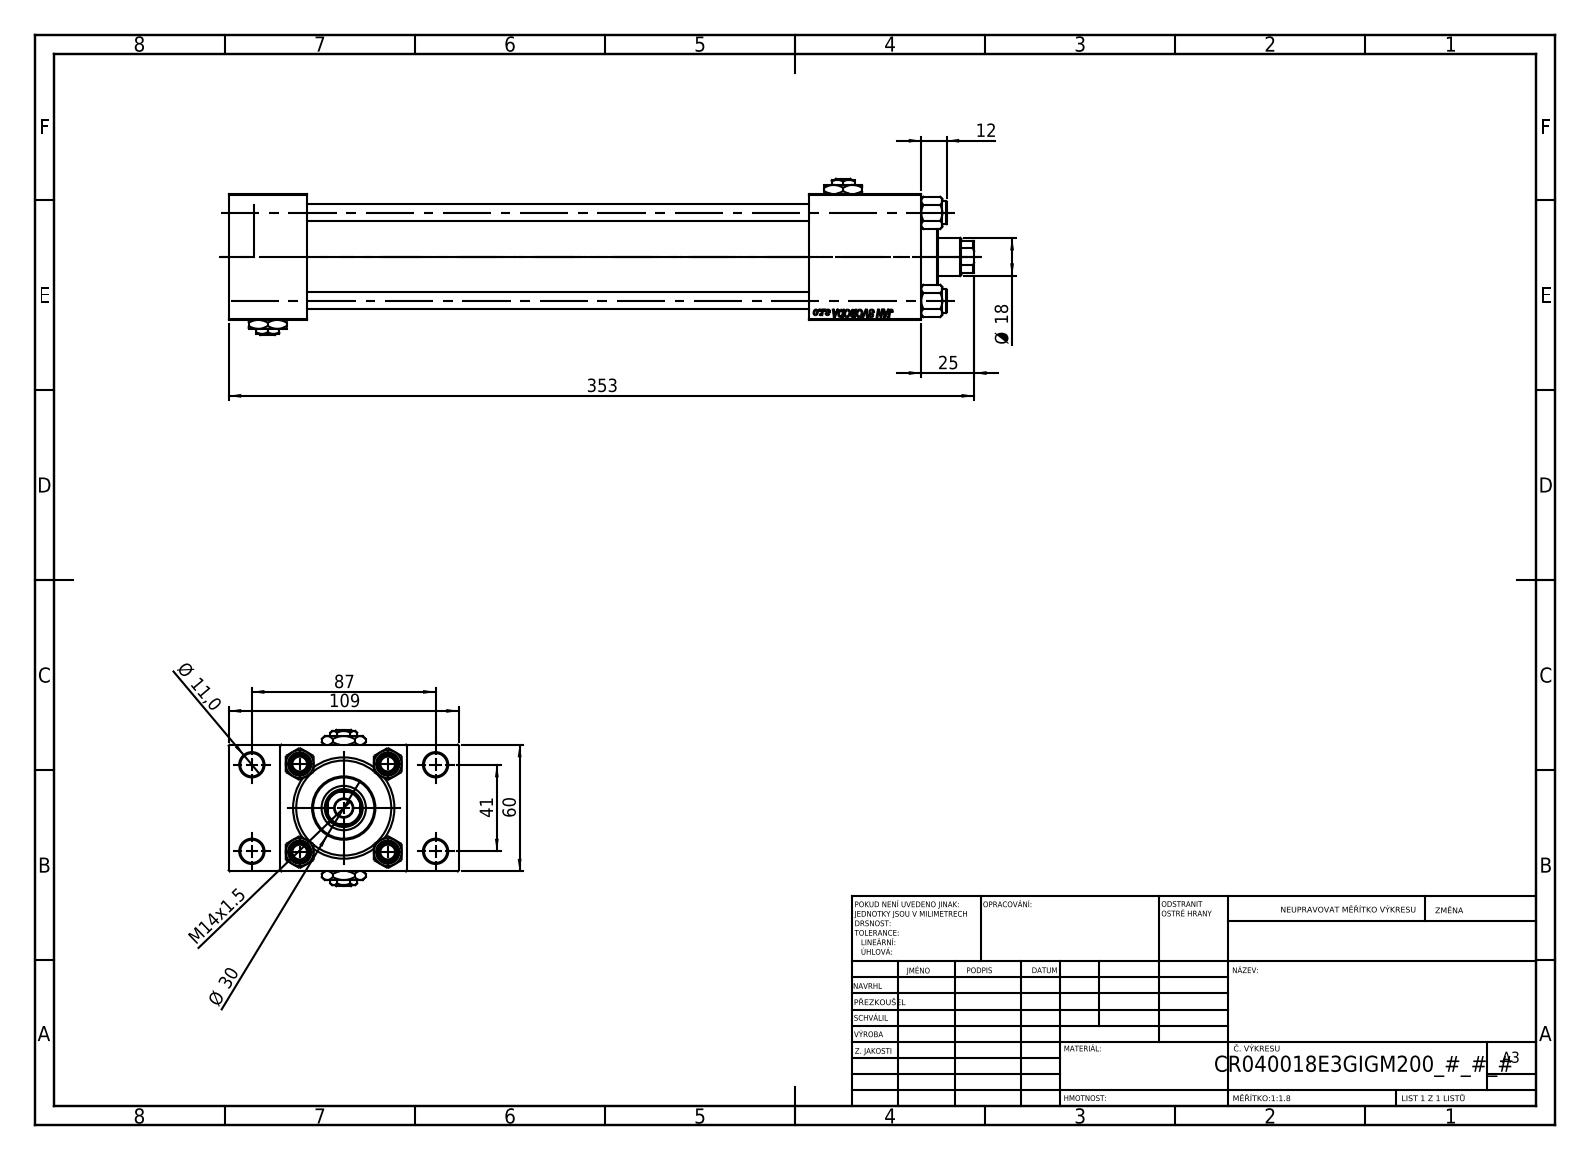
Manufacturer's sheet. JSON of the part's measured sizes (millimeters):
{"part_name": "NUT_M5_E; V215CR_TYCINKA_E; V215CR_VCP_E; V215_VC_A (+2 more)", "step_written_by": "SolidWorks 2019 (CONFIG_CONTROL_DESIGN)", "units": "millimeters", "bodies": {"solids": 13, "faces": 1231, "planar": 544, "cylindrical": 93, "other": 594}, "overall_size": [353, 109, 74], "volume_mm3": 654484, "surface_area_mm2": 203919, "round_holes": [[8, 4], [11, 4], [7, 3], [16.66, 3], [24, 3], [8.5, 1], [18, 1], [21, 1], [31, 1], [40, 1], [45, 1]], "round_bosses_or_shafts": [[11, 4], [46, 1], [30, 1]], "partial_cylinders_radius": [[8.5, 1]], "face_to_face_distances": [60, 37, 24.5, 84.5, 328, 291, 24.3, 53, 275, 238], "hole_center_spacings": [22.65, 29.49, 41.7, 47.15, 48.09, 64.35, 76.49, 41]}
